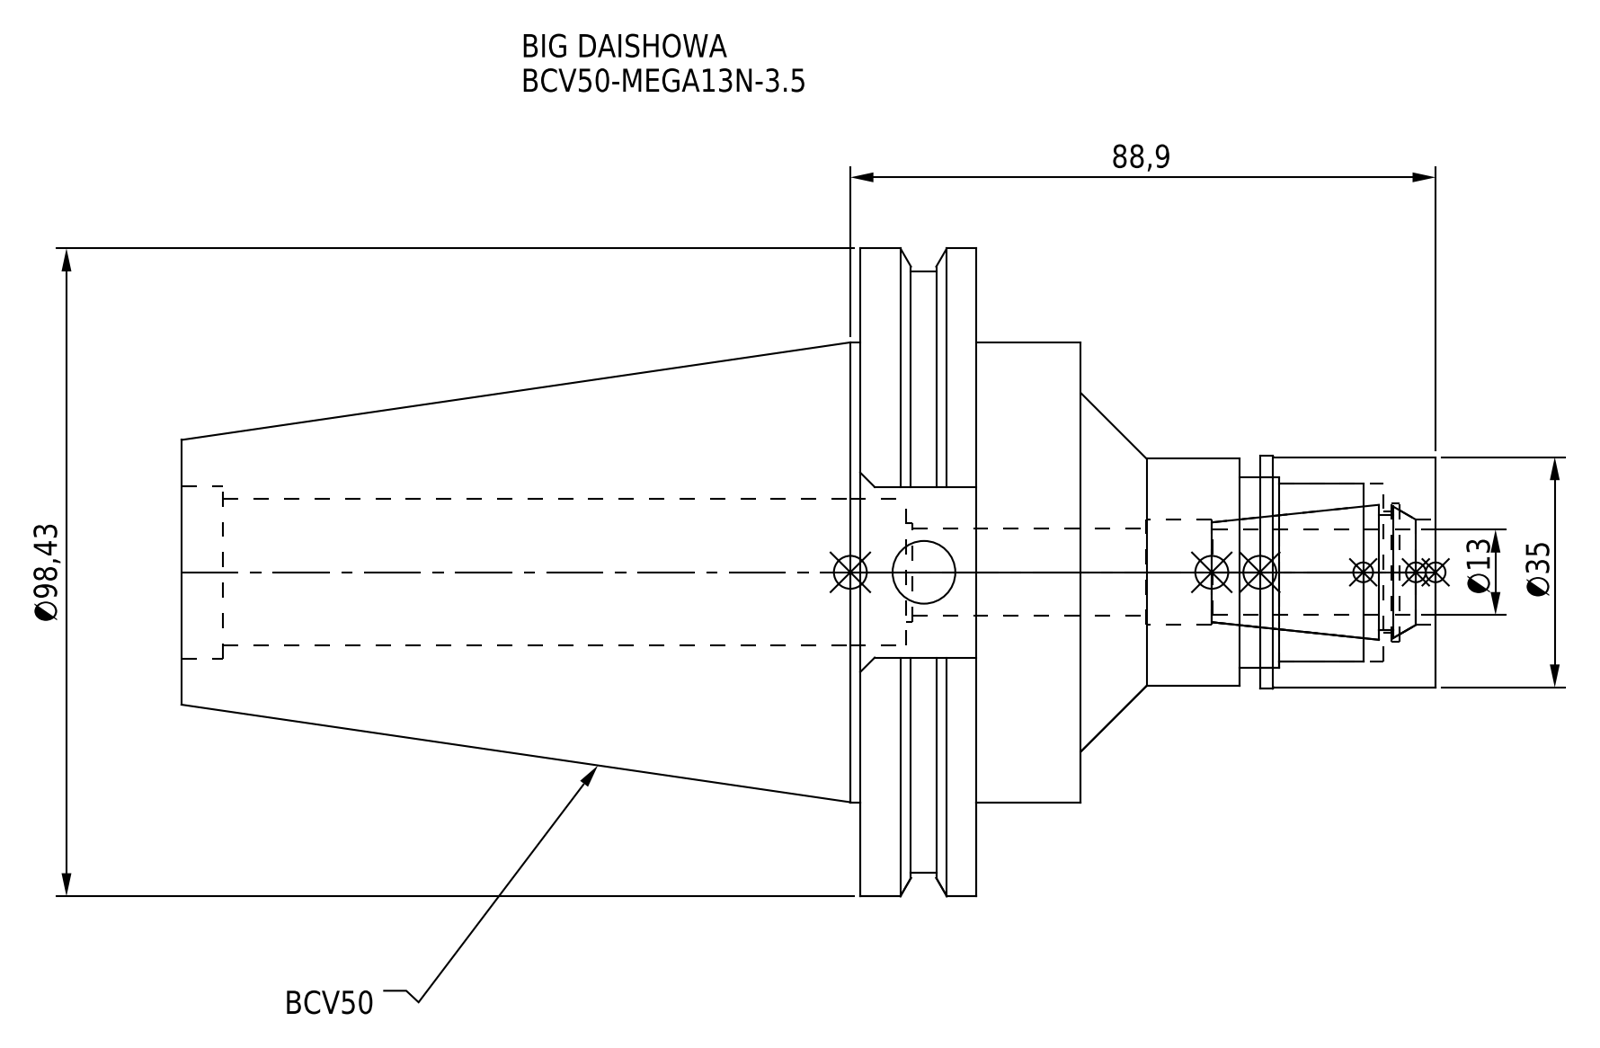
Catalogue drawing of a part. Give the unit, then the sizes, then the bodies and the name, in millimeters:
Units: millimetres
Overall size (bounding box): 190.5 × 98.42 × 94.95
Round holes (diameter × count): ⌀9.53 ×1, ⌀13.3 ×1, ⌀15 ×1, ⌀16 ×1, ⌀18.5 ×1, ⌀21 ×1, ⌀22.3 ×1, ⌀26.23 ×1, ⌀27 ×1, ⌀29 ×1
Round bosses / shafts (diameter × count): ⌀98.42 ×1, ⌀91.29 ×1, ⌀69.85 ×1, ⌀35.3 ×1, ⌀35 ×1, ⌀34.5 ×1
Main face-to-face distances: 17.55, 15.95, 33.5, 53.9, 69.85, 87.4, 190.5, 136.6, 120.65, 103.1
Volume: 428 664 mm³ · Surface area: 61 187 mm²
Bodies: 2 solids, 91 faces (33 planar, 44 cylindrical, 14 other)
Part name (STEP PRODUCT): BCV50-MEGA13N-3_5-130-FreeParts; BCV50-MEGA13N-3_5; BCV50MN13035-130_ASM.stp; BCV50-MEGA13N-3_5-130.stp (+3 more)
STEP written by: SolidWorks 2019 (CONFIG_CONTROL_DESIGN)
